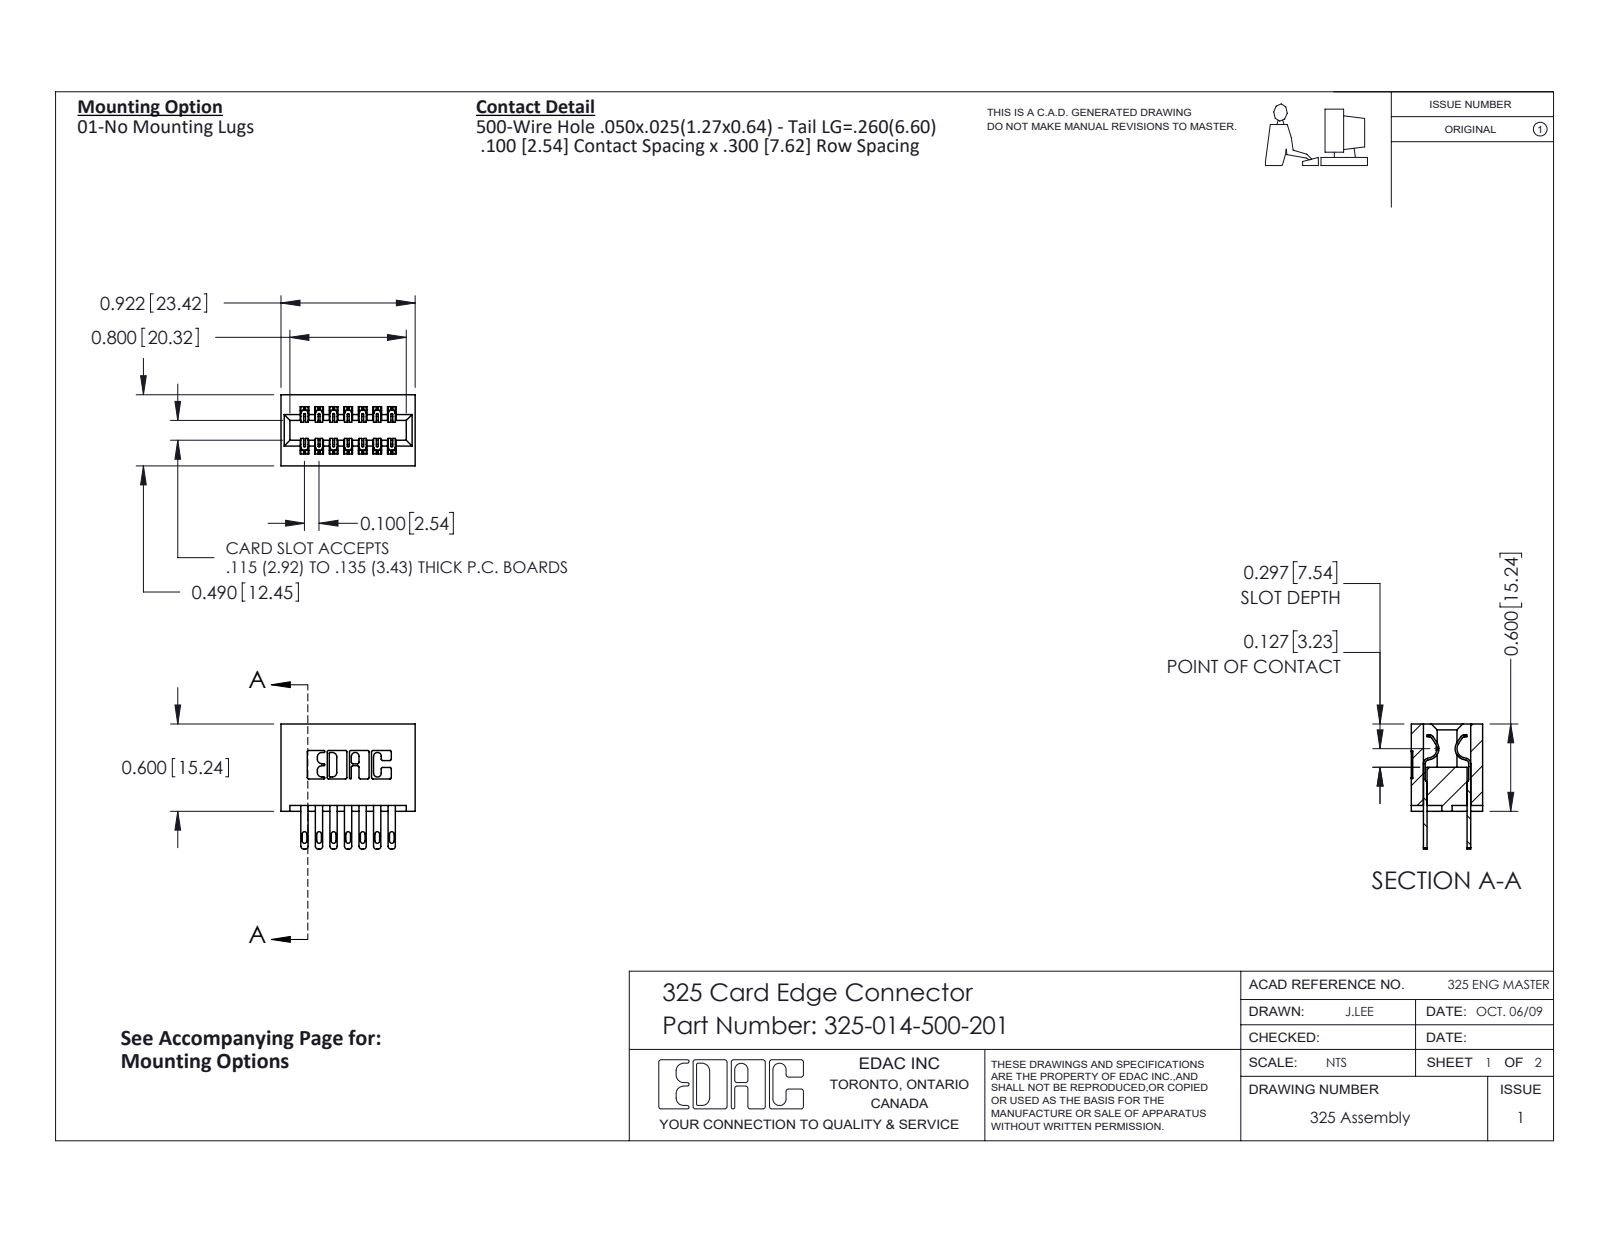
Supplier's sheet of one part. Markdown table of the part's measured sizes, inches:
| quantity | value |
| --- | --- |
| part name | 325 Part_Lugless; 325-014-500-201; 325-292-001_325-293-100 |
| STEP written by | SolidWorks 2016 (CONFIG_CONTROL_DESIGN) |
| units | inches |
| bodies | 15 solids, 778 faces (486 planar, 292 cylindrical, 0 other) |
| overall size | 0.922 × 0.86 × 0.49 |
| volume | 0.205 in³ |
| surface area | 6.265 in² |
| partial cylindrical surfaces (radius × count) | 0.01 × 22, 0.006 × 21, 0.016 × 14, 0.02 × 14, 0.007 × 6, 0.031 × 6, 0.026 × 3, 0.014 × 2 |
| main face-to-face distances | 0.3, 0.1, 0.083, 0.407, 0.2, 0.04, 0.107, 0.383, 0.025, 0.06 |
